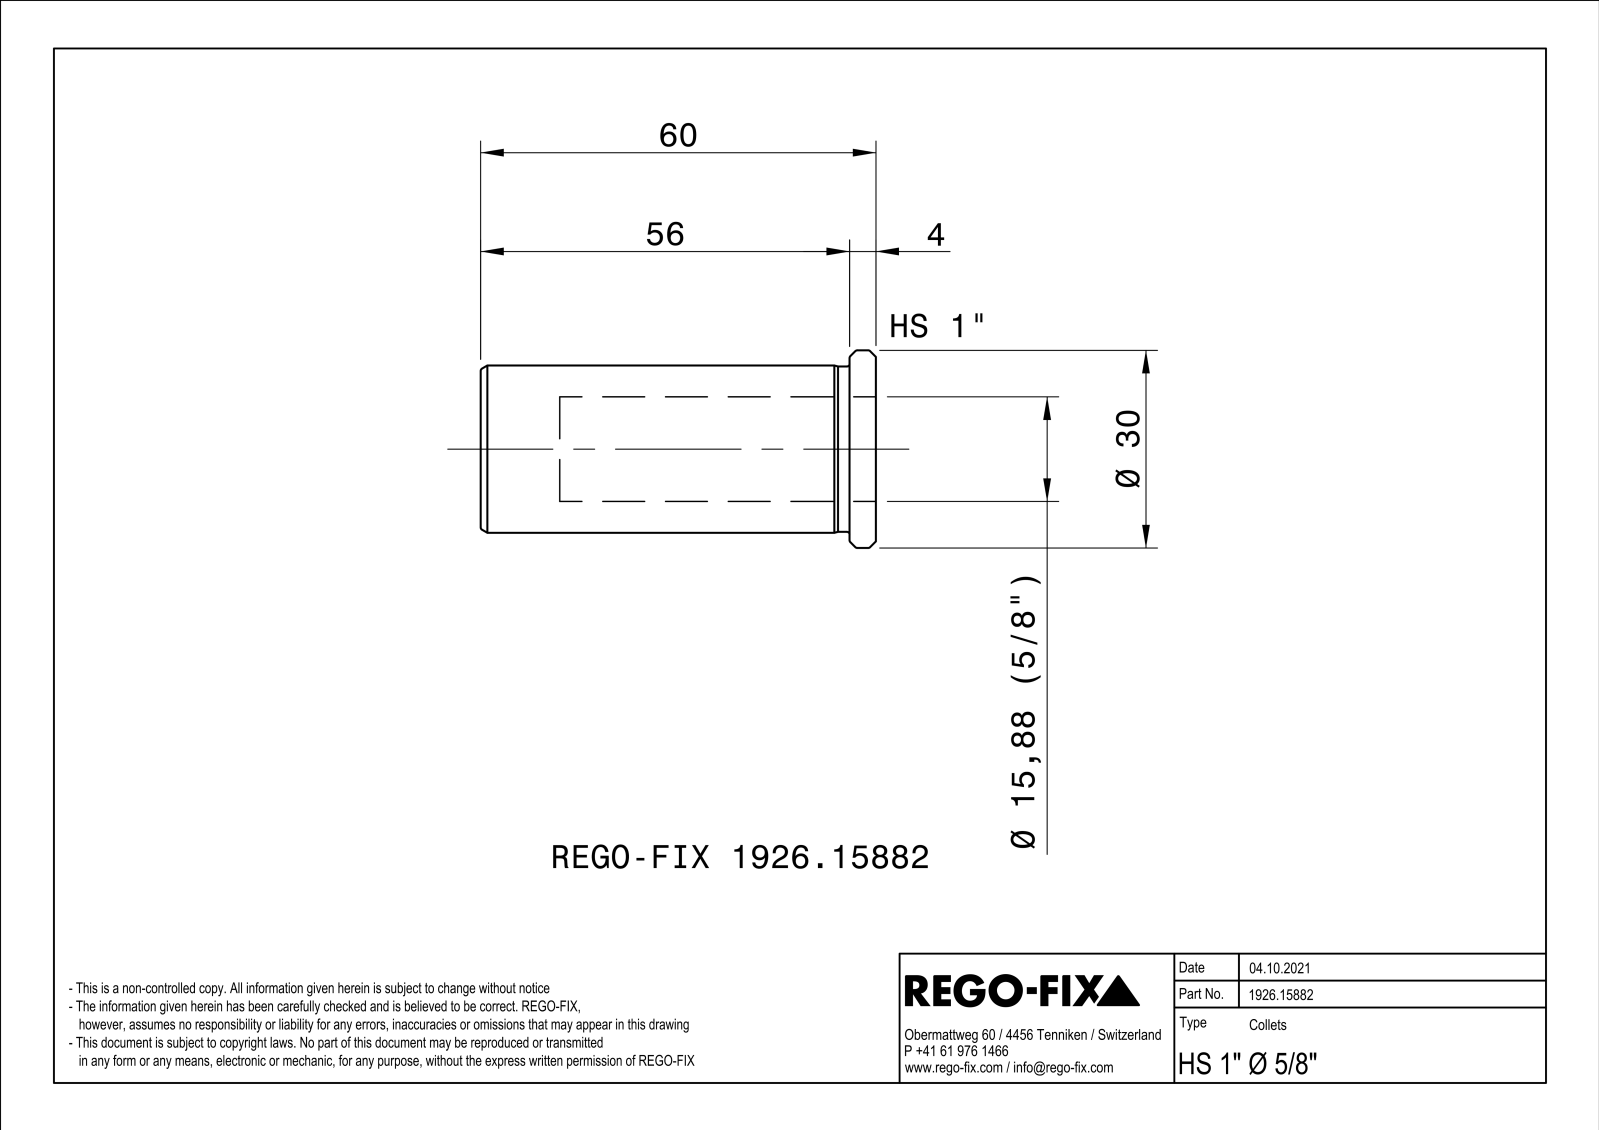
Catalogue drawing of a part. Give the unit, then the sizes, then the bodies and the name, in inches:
Units: inches
Overall size (bounding box): 2.362 × 1.18 × 1.18
Round holes (diameter × count): ⌀0.625 ×1, ⌀0.807 ×1
Round bosses / shafts (diameter × count): ⌀1.181 ×1, ⌀1 ×1, ⌀0.988 ×1
Main face-to-face distances: 0.039, 2.362, 0.157, 2.205
Volume: 1.034 in³ · Surface area: 15.52 in²
Bodies: 1 solid, 70 faces (22 planar, 11 cylindrical, 37 other)
Part name (STEP PRODUCT): NOCUT
STEP written by: SIEMENS PLM Software Solid Edge ST10 (AUTOMOTIVE_DESIGN)
